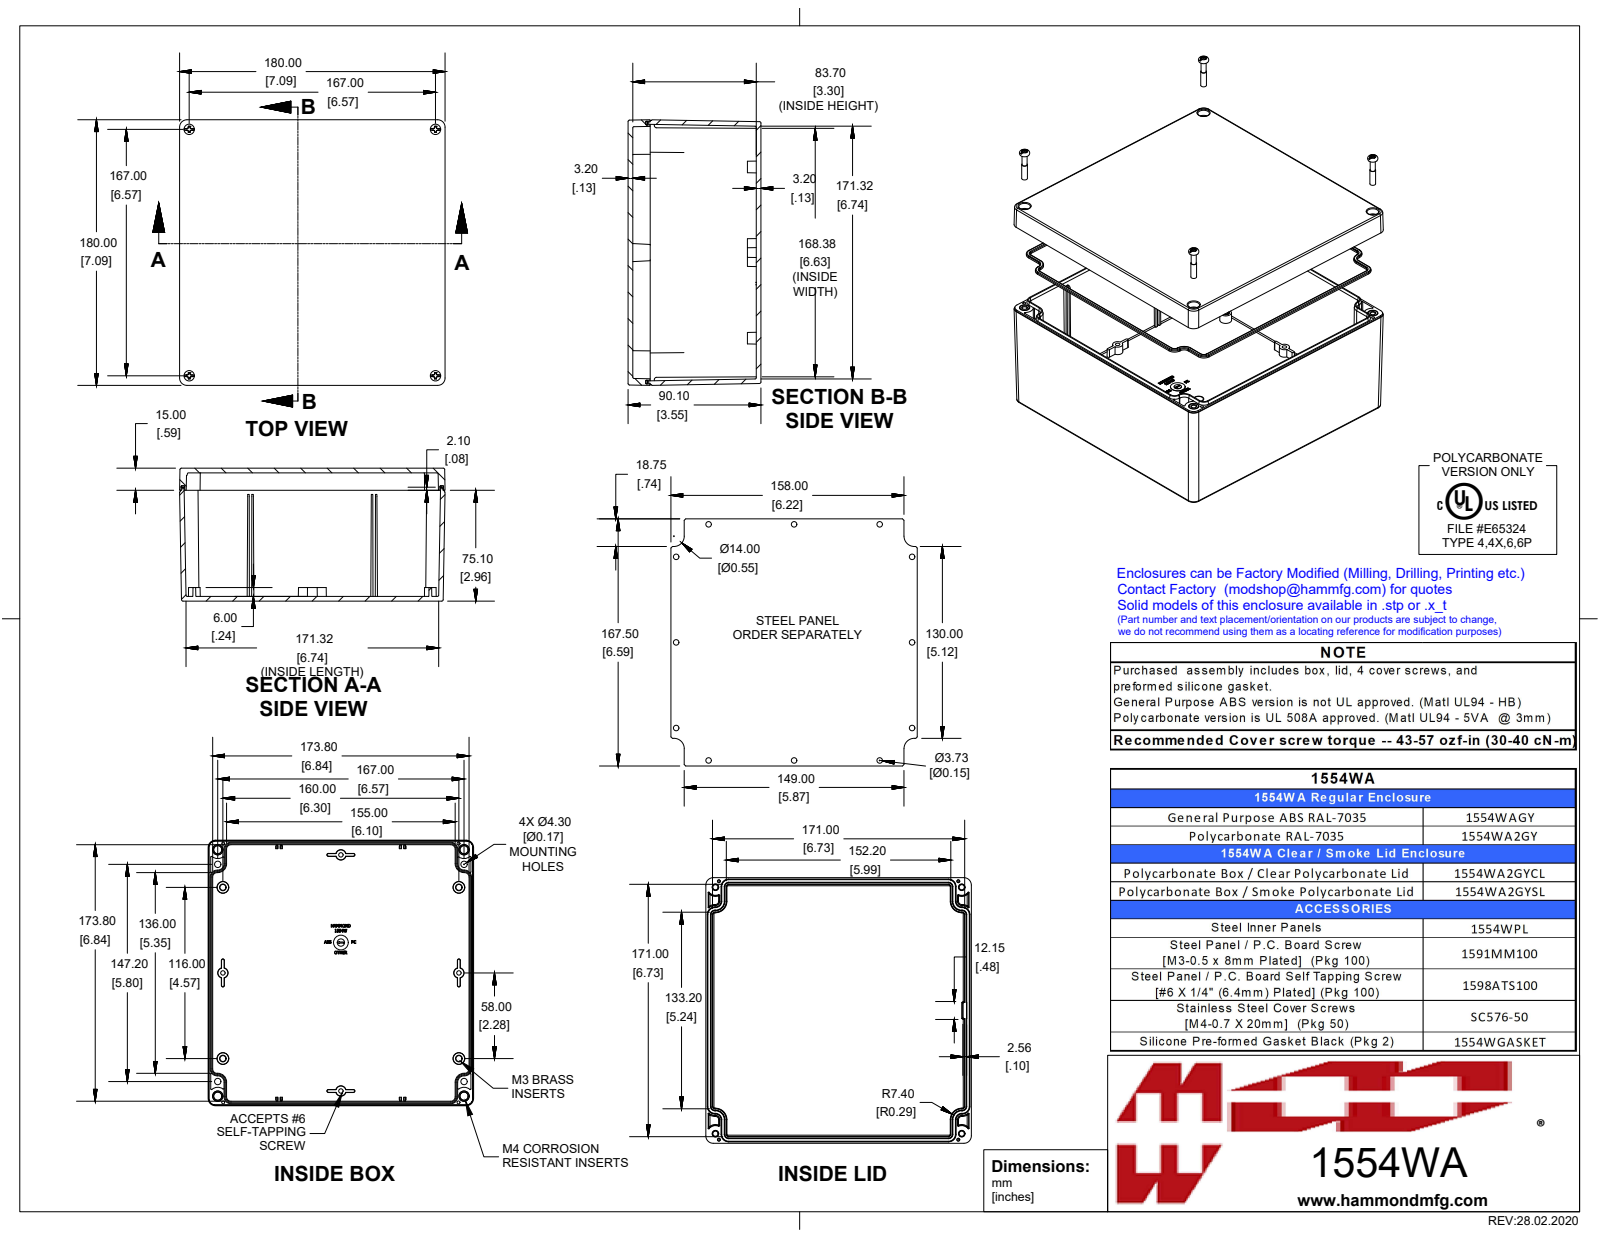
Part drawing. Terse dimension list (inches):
name: 1554WAGY
written by: SolidWorks 2019 (AUTOMOTIVE_DESIGN)
unit: in
bodies: 15 solids, 1862 faces (623 planar, 378 cylindrical, 861 other)
size: 7.087 × 7.087 × 3.547
volume: 25.76 in³; area: 437.7 in²
holes: 4× ⌀0.097, 4× ⌀0.128, 4× ⌀0.181
bosses: 4× ⌀0.25, 4× ⌀0.218, 4× ⌀0.21, 4× ⌀0.19, 4× ⌀0.154, 4× ⌀0.153, 4× ⌀0.15, 4× ⌀0.135
rounds: 26× R0.02, 20× R0.012, 12× R0.039, 10× R0.031, 8× R0.104, 8× R0.118, 8× R0.197, 8× R0.199
face distances: 0.126, 3.421, 0.122, 3.547, 3.295, 7.087, 6.965, 6.909, 6.787, 0.177
hole spacings: 1.013, 5.572, 6.515, 6.575, 8.513, 4.567, 6.299, 7.781
